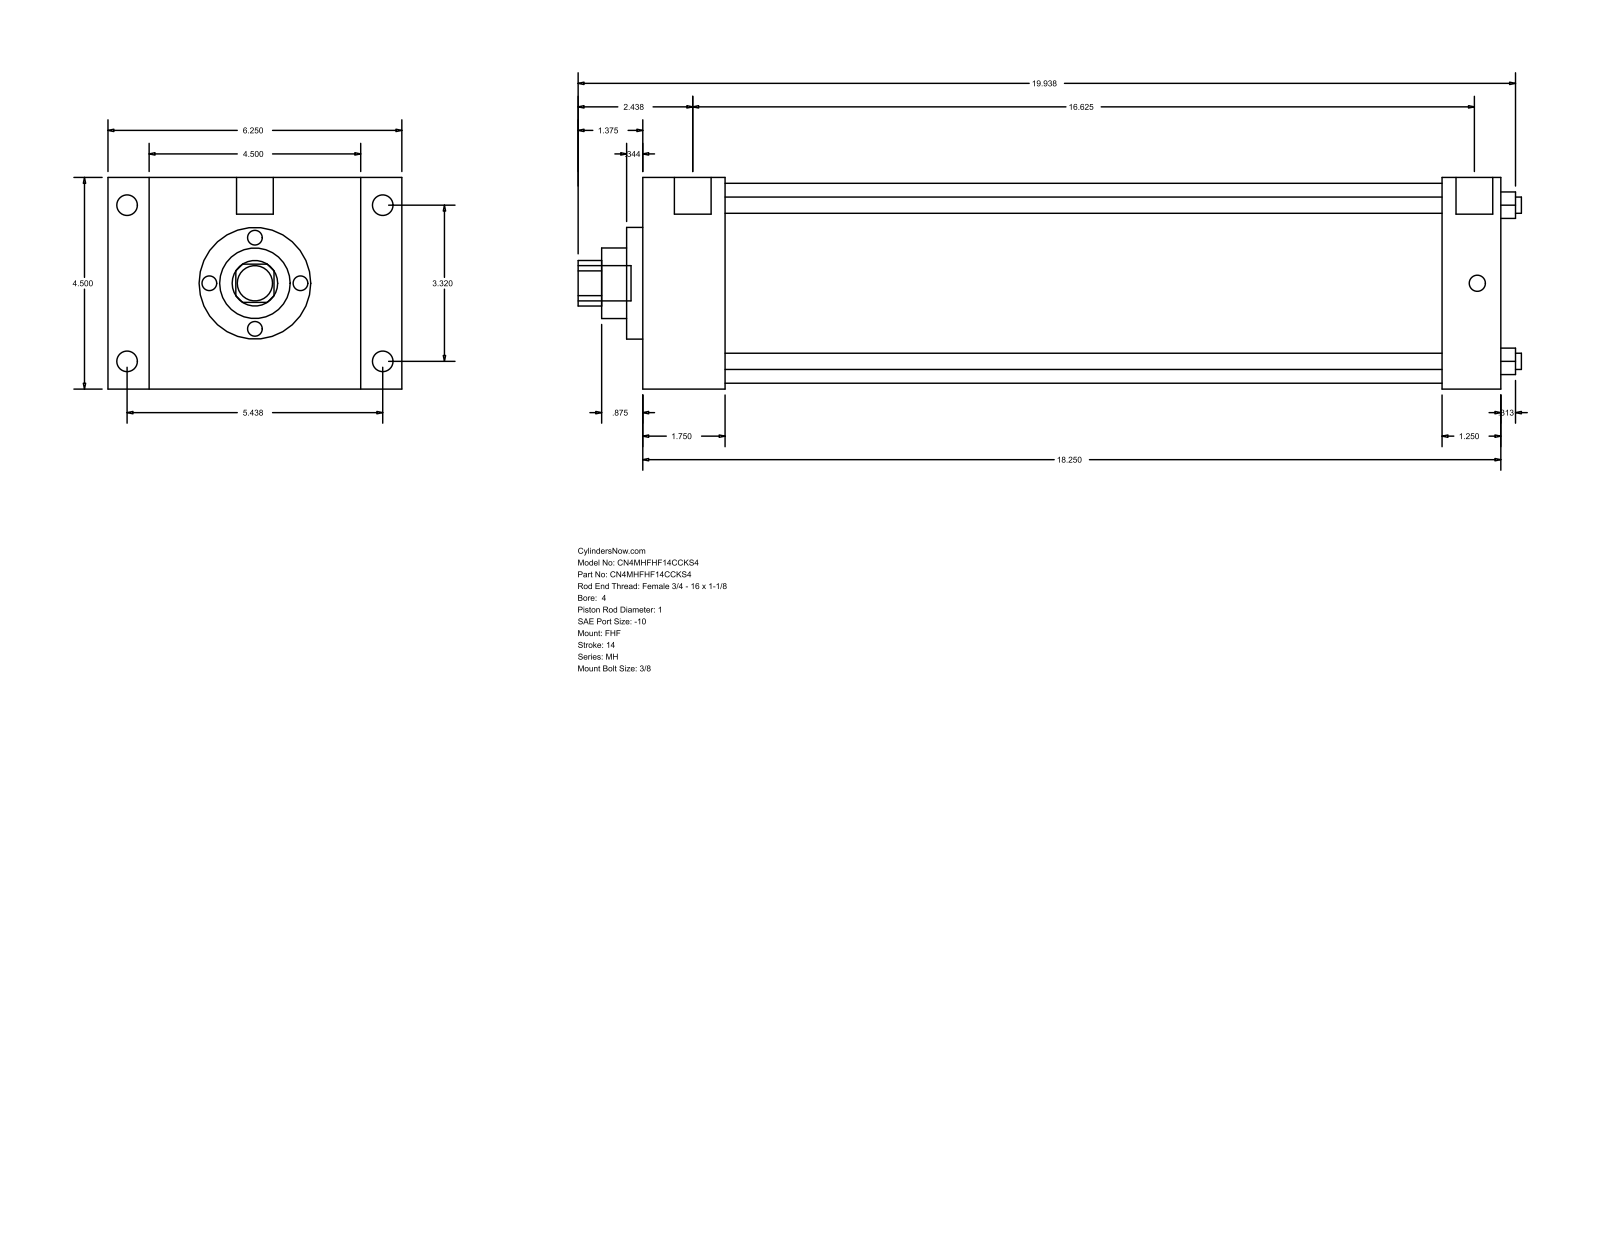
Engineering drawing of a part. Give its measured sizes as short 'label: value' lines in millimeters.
name: MH_FHF__0400_1
written by: GSSL Pune (CONFIG_CONTROL_DESIGN)
unit: mm
bodies: 0 solids, 90 faces (61 planar, 29 cylindrical, 0 other)
size: 509.59 × 158.75 × 114.3
holes: 4× ⌀8.76, 1× ⌀25.4, 1× ⌀38.1, 1× ⌀60.33, 1× ⌀107.95
bosses: 4× ⌀11.13, 4× ⌀8.73, 2× ⌀19.84, 1× ⌀19.05
rounds: 1× R12.29
face distances: 114.3, 463.56, 44.46, 419.1, 22.23, 136.53, 158.76, 431.81, 387.35, 31.75
hole spacings: 59.62, 84.32, 119.25
